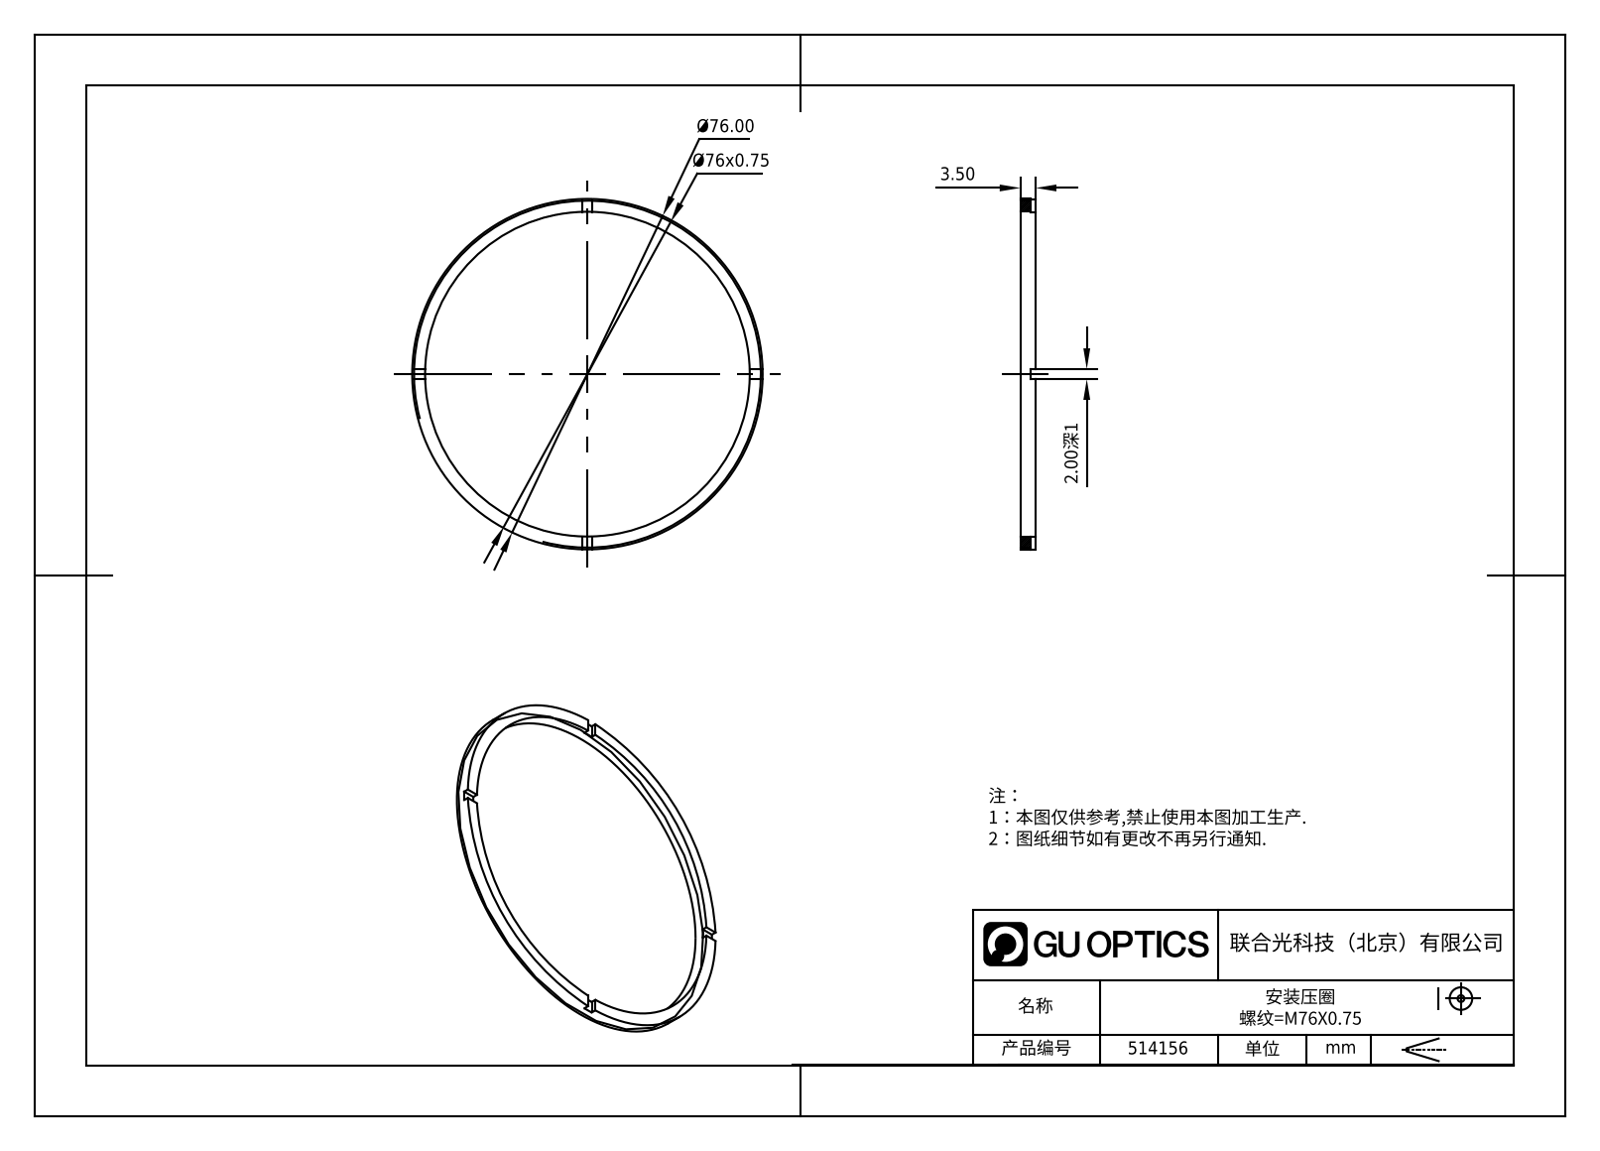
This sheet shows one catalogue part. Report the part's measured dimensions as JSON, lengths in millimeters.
{"part_name": "514156", "step_written_by": "SolidWorks 2020 (CONFIG_CONTROL_DESIGN)", "units": "millimeters", "bodies": {"solids": 1, "faces": 21, "planar": 17, "cylindrical": 4, "other": 0}, "overall_size": [76, 76, 3.5], "volume_mm3": 2384, "surface_area_mm2": 2989, "round_holes": [[70, 1]], "round_bosses_or_shafts": [[76, 1]], "face_to_face_distances": [3.5, 2.5, 1, 2]}
